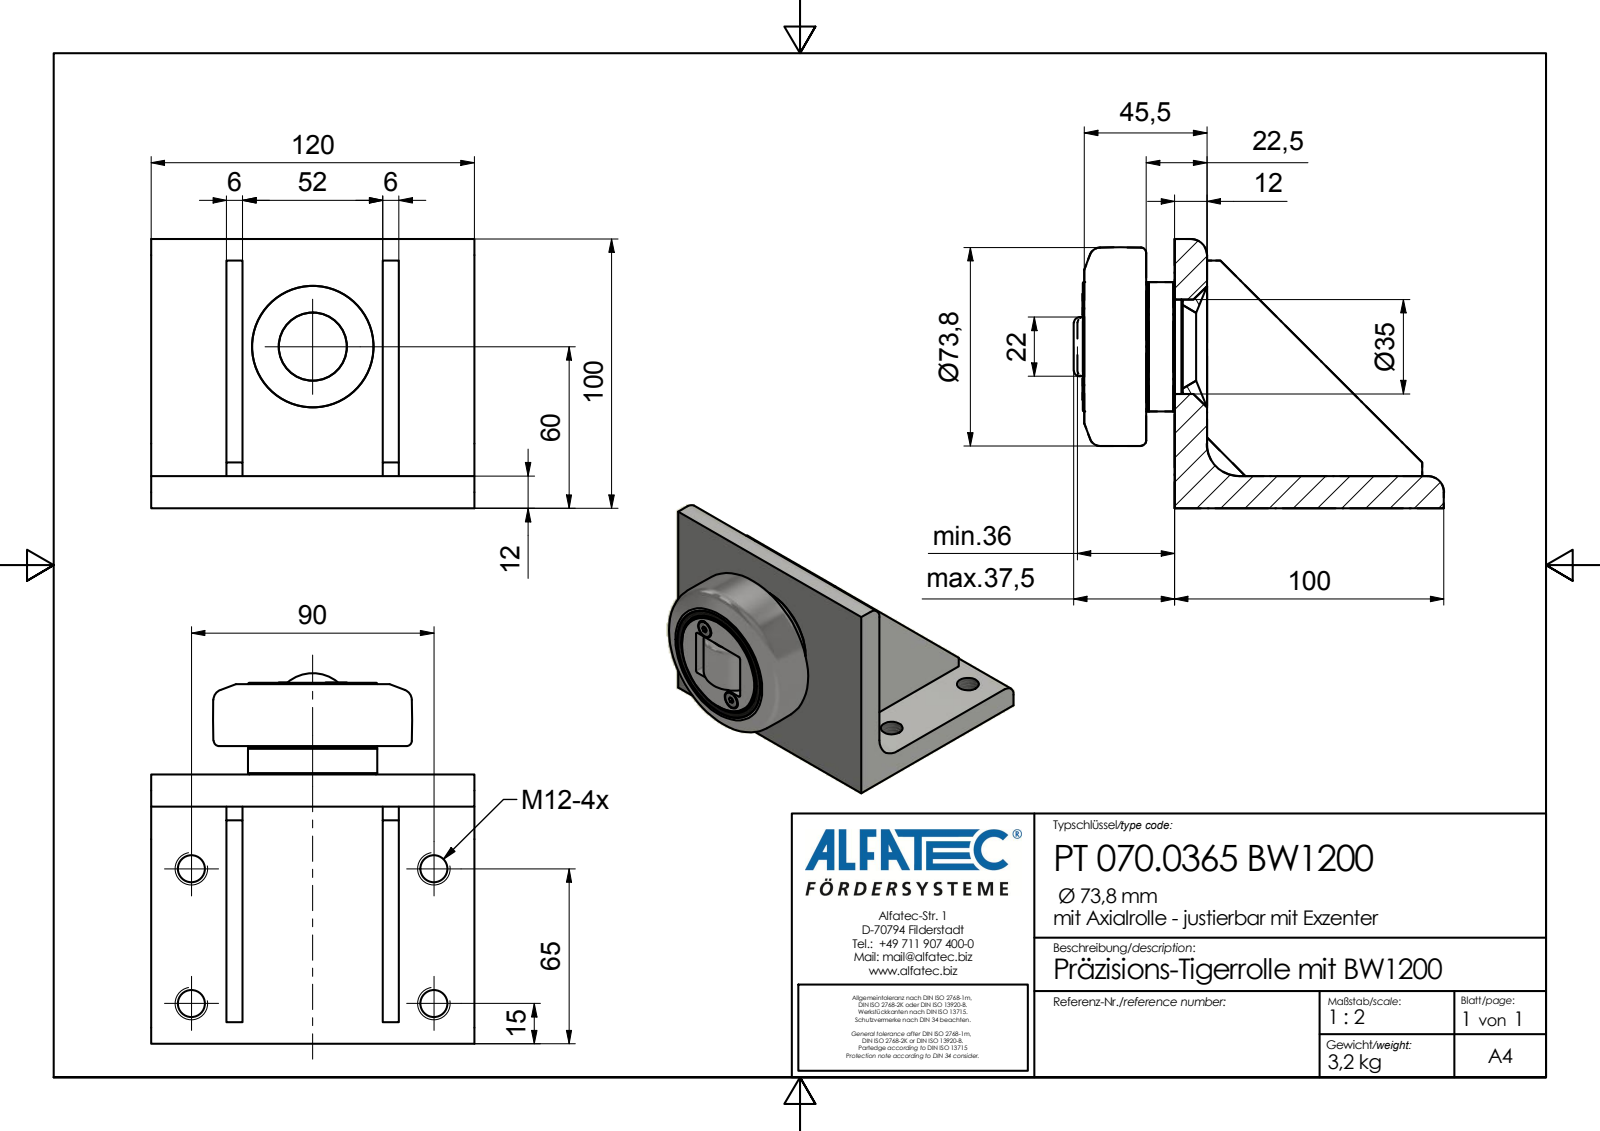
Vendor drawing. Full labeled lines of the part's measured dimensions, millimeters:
Part name (STEP PRODUCT): PT 070.0365 BW1200_Kontur
STEP written by: Autodesk Inventor 2020 (AP242_MANAGED_MODEL_BASED_3D_ENGINEERING_MIM_LF)
Units: millimetres
Bodies: 1 solid, 81 faces (50 planar, 18 cylindrical, 13 other)
Overall size (bounding box): 137.5 × 120 × 100
Volume: 422 239 mm³ · Surface area: 77 629 mm²
Round holes (diameter × count): ⌀10.11 ×4
Round bosses / shafts (diameter × count): ⌀7.8 ×2, ⌀48 ×1
Partial cylindrical surfaces — rounded edges, fillets, slot ends (radius × count): R1 ×4, R6 ×2, R11 ×1, R12 ×1
Main face-to-face distances: 12, 58, 6, 34, 92, 28, 86, 64, 52, 120
Hole centre spacings: 50, 90, 102.96
